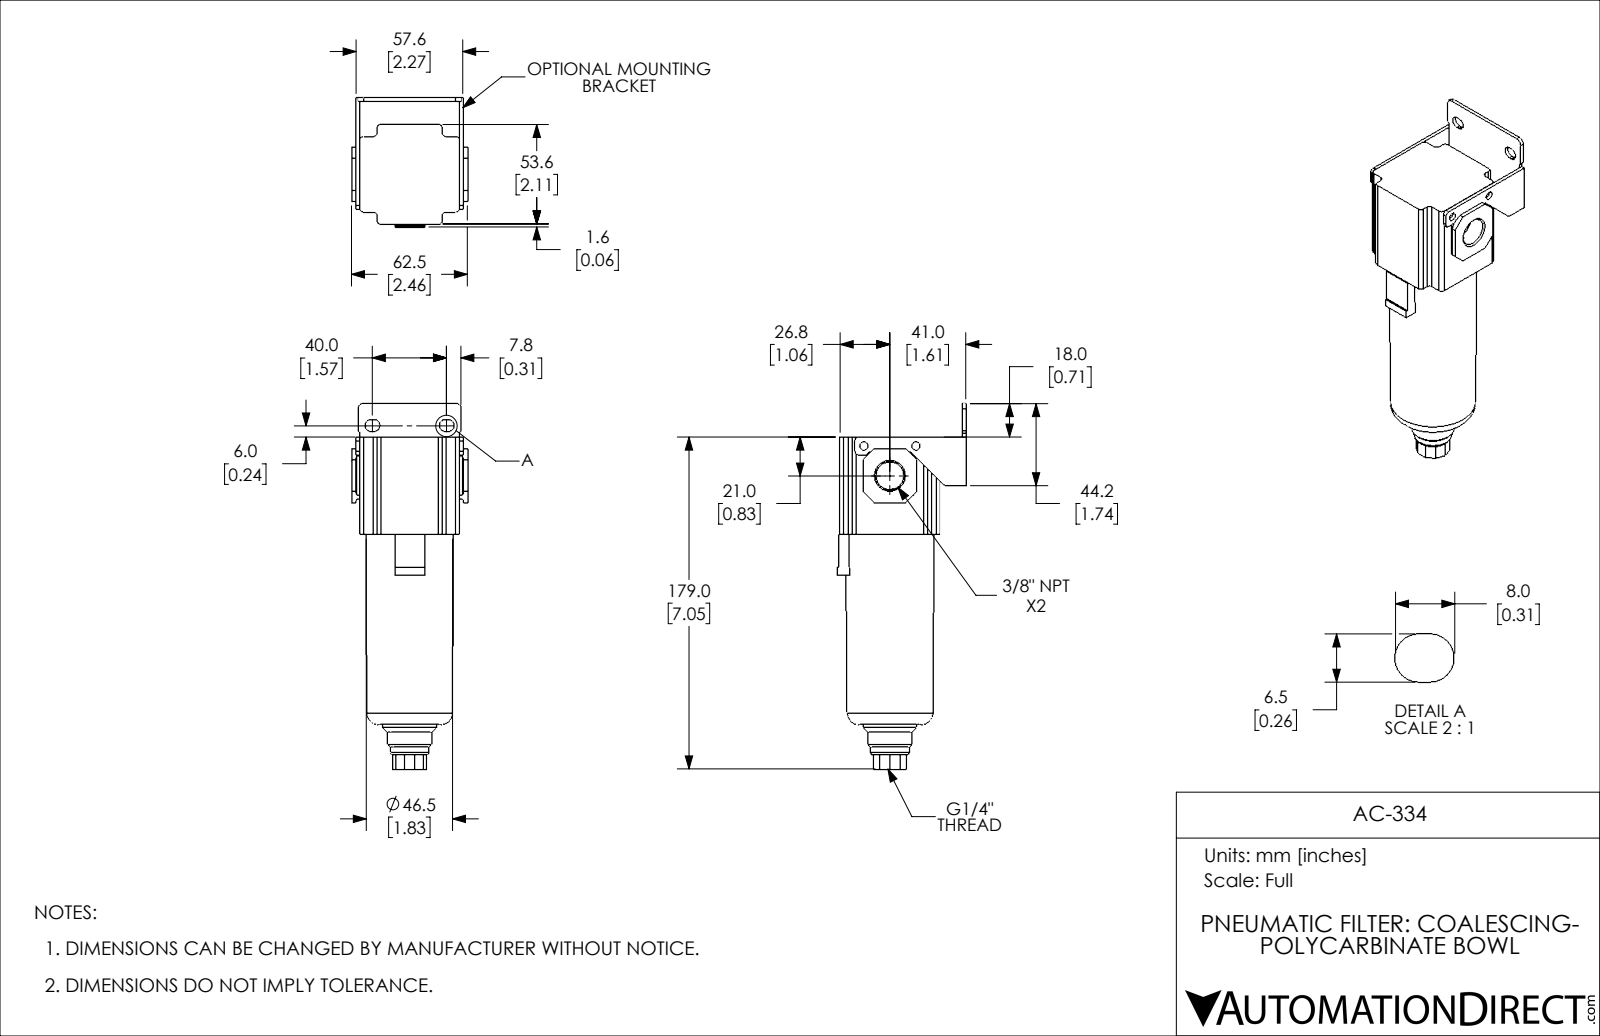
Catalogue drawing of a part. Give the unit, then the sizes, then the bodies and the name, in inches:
Units: inches
Overall size (bounding box): 7.756 × 2.733 × 2.461
Round holes (diameter × count): ⌀0.177 ×2, ⌀0.451 ×1, ⌀0.589 ×1
Round bosses / shafts (diameter × count): ⌀1.102 ×1, ⌀0.906 ×1, ⌀0.787 ×1
Partial cylindrical surfaces — rounded edges, fillets, slot ends (radius × count): R0.079 ×15, R0.128 ×4, R0.039 ×2, R0.118 ×2
Main face-to-face distances: 0.079, 2.11, 2.189, 0.559, 2.669, 0.48, 2.591, 2.067, 0.258, 1.852
Hole centre spacings: 0.837, 1.102
Volume: 19.92 in³ · Surface area: 65.58 in²
Bodies: 1 solid, 173 faces (109 planar, 48 cylindrical, 16 other)
Part name (STEP PRODUCT): AC-334
STEP written by: SolidWorks 2018 (AUTOMOTIVE_DESIGN)
